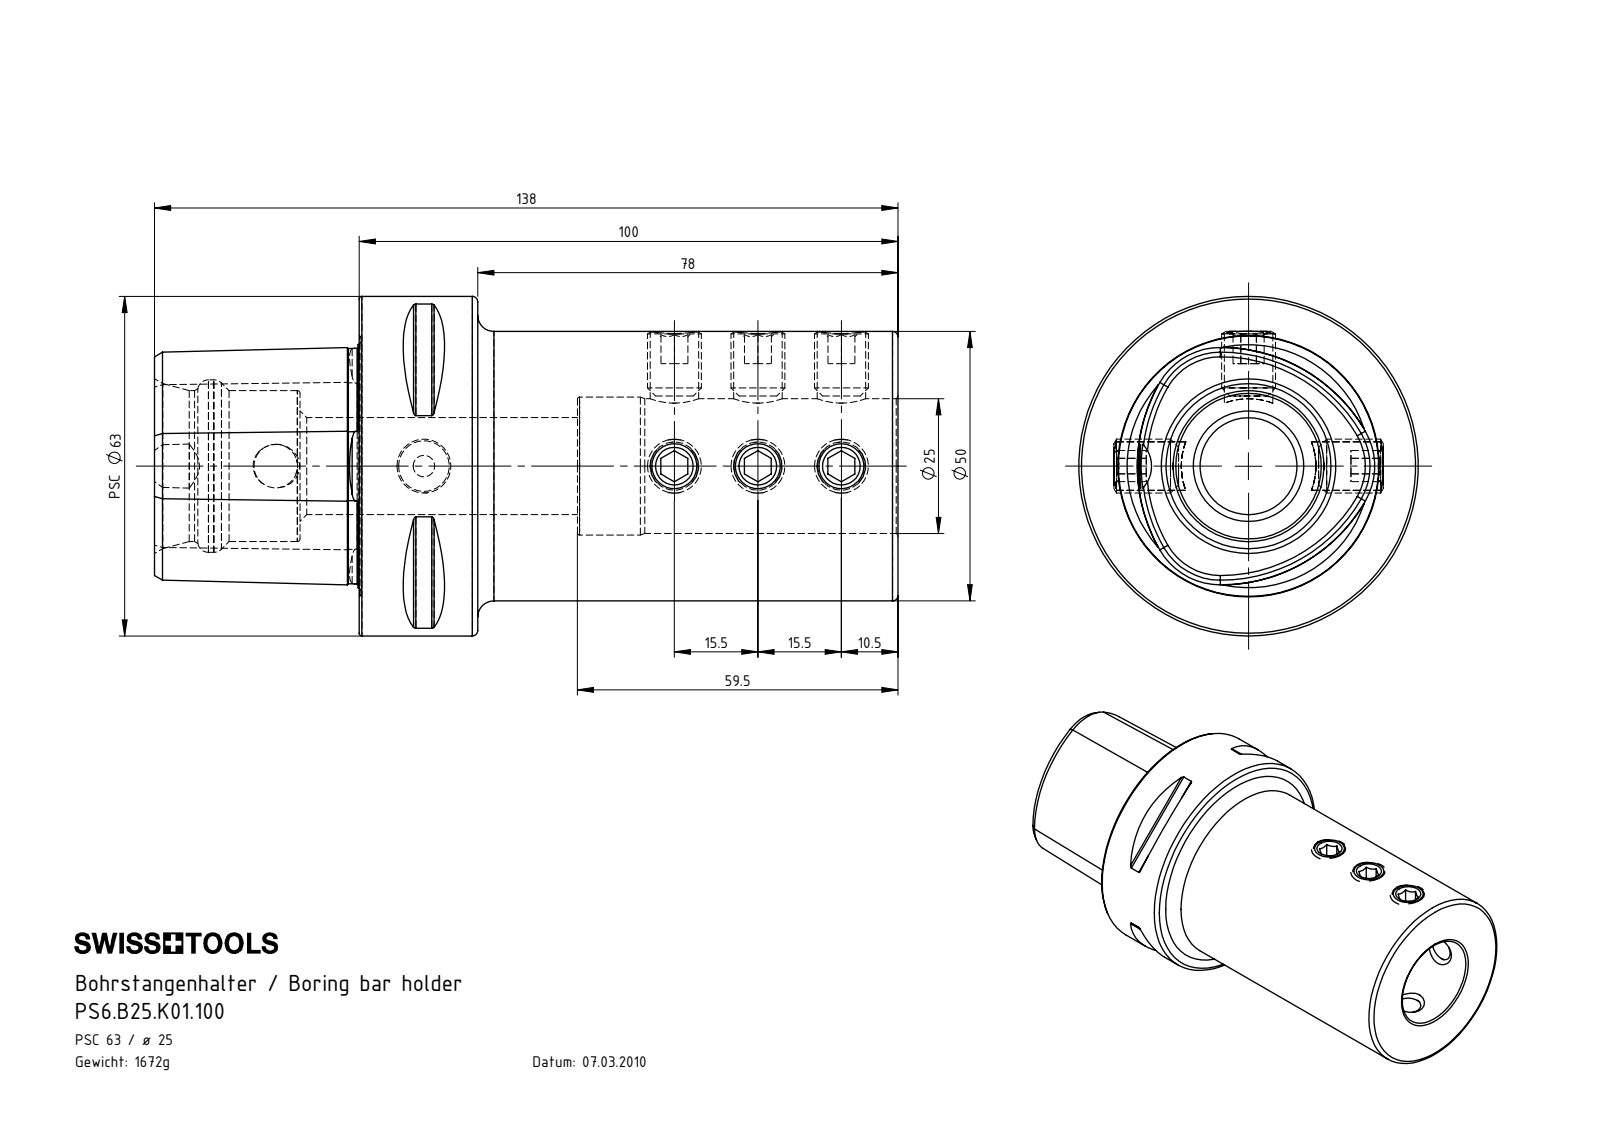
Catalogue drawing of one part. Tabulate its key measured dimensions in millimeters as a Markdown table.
| quantity | value |
| --- | --- |
| part name | ISO 4026 - M10 x 12_PreviewCfg; PS6-B25.K01.100_B; PS6.B25.K01.100 |
| STEP written by | SolidWorks 2017 (AUTOMOTIVE_DESIGN) |
| units | millimeters |
| bodies | 10 solids, 304 faces (102 planar, 67 cylindrical, 135 other) |
| overall size | 138 × 63 × 63 |
| volume | 213 400 mm³ |
| surface area | 44 803 mm² |
| round holes (diameter × count) | 9 × 6, 4 × 1, 8.1 × 1, 18 × 1, 25 × 1, 25.6 × 1, 28 × 1, 32 × 1 |
| round bosses / shafts (diameter × count) | 10 × 6, 63 × 1, 50 × 1 |
| partial cylindrical surfaces (radius × count) | 0.5 × 8, 6 × 1 |
| main face-to-face distances | 100, 38, 22, 78, 60, 138, 15.5, 5, 7.75, 6 |
| hole center spacings | 15.5, 31, 27.5, 46.5, 62, 74, 77.5, 89.5 |
